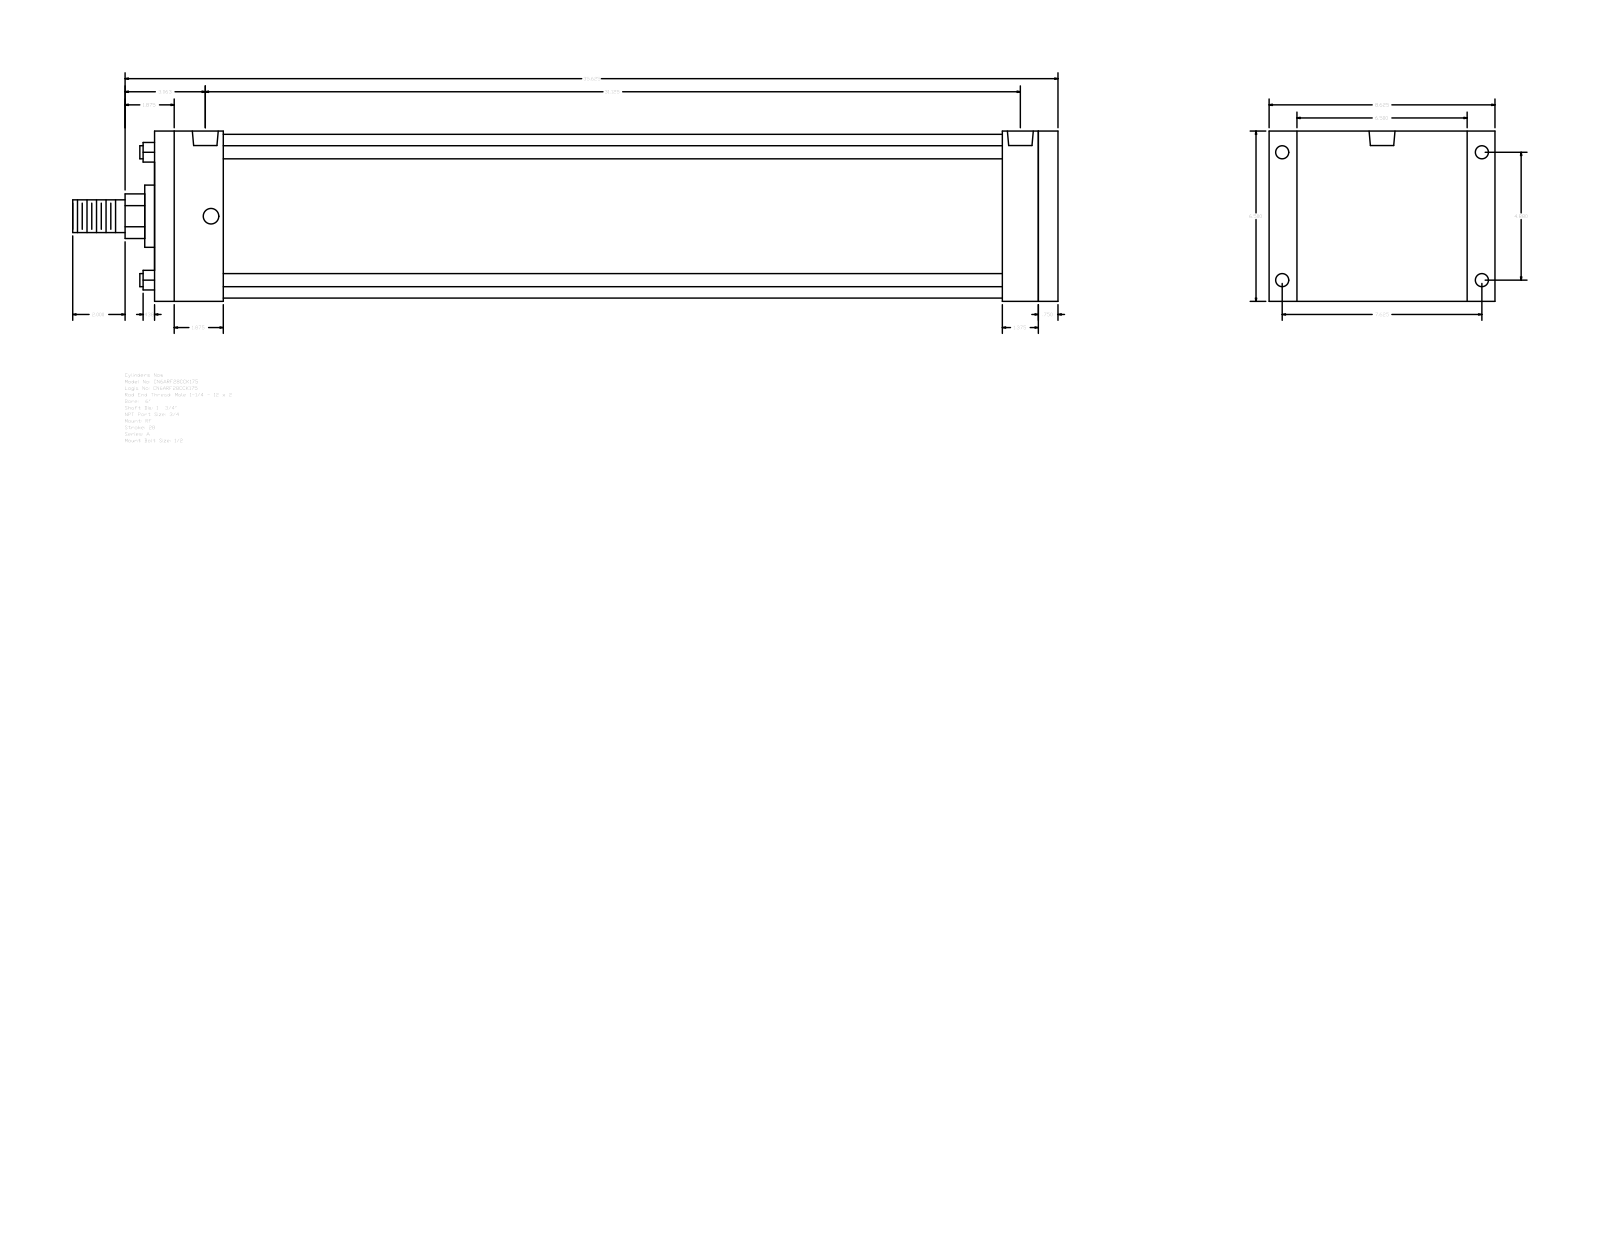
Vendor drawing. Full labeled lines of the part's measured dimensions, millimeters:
Part name (STEP PRODUCT): A_RF__0600_1.75
STEP written by: GSSL Pune (CONFIG_CONTROL_DESIGN)
Units: millimetres
Bodies: 0 solids, 92 faces (64 planar, 28 cylindrical, 0 other)
Overall size (bounding box): 955.67 × 219.07 × 165.1
Round holes (diameter × count): ⌀12.7 ×4, ⌀15.08 ×4, ⌀25.12 ×2
Round bosses / shafts (diameter × count): ⌀12.7 ×4, ⌀158.75 ×1, ⌀60.33 ×1, ⌀44.45 ×1, ⌀31.75 ×1
Partial cylindrical surfaces — rounded edges, fillets, slot ends (radius × count): R21.63 ×1
Main face-to-face distances: 165.1, 876.31, 19.05, 857.26, 66.68, 790.58, 809.63, 822.33, 755.65, 34.93
Hole centre spacings: 5.56, 123.96, 193.68, 229.95, 779.45, 785.01, 790.57
